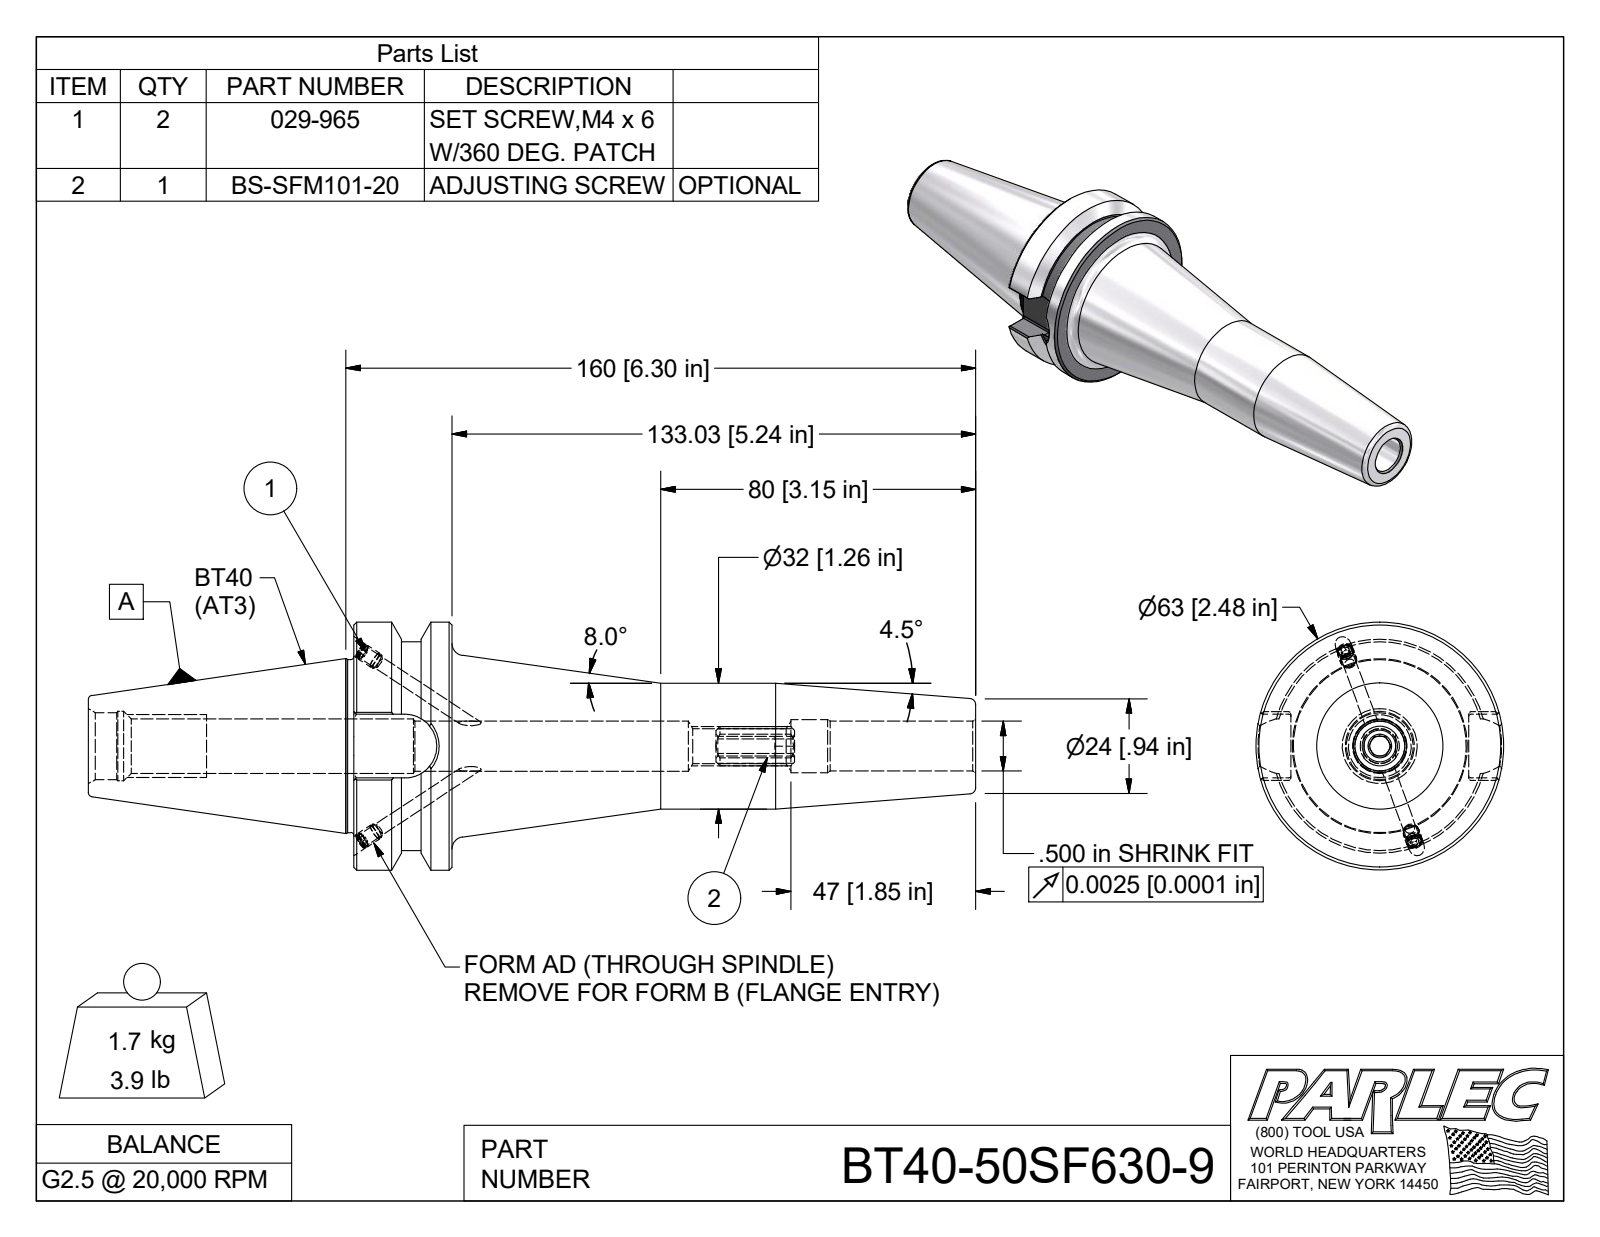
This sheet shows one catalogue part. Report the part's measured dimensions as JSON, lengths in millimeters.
{"part_name": "BT40-50SF630-9; BT40BC-50SF630-9-1; 029-965; BS-SFM101-20", "step_written_by": "Autodesk Inventor 2009 (AUTOMOTIVE_DESIGN)", "units": "millimeters", "bodies": {"solids": 4, "faces": 134, "planar": 57, "cylindrical": 33, "other": 44}, "overall_size": [225.4, 63, 63], "volume_mm3": 225500, "surface_area_mm2": 41920, "round_holes": [[3.3, 2], [4.1, 2], [12.7, 1], [13.4, 1], [17.6, 1]], "round_bosses_or_shafts": [[4.2, 2], [4, 2], [63, 1], [53, 1], [44.5, 1], [43.9, 1], [32, 1]], "partial_cylinders_radius": [[0.5, 8], [5, 1], [8.1, 1]], "face_to_face_distances": [25, 45.2, 18.6, 26.6, 158, 133, 67.4, 92.4, 225.4, 16.2]}
